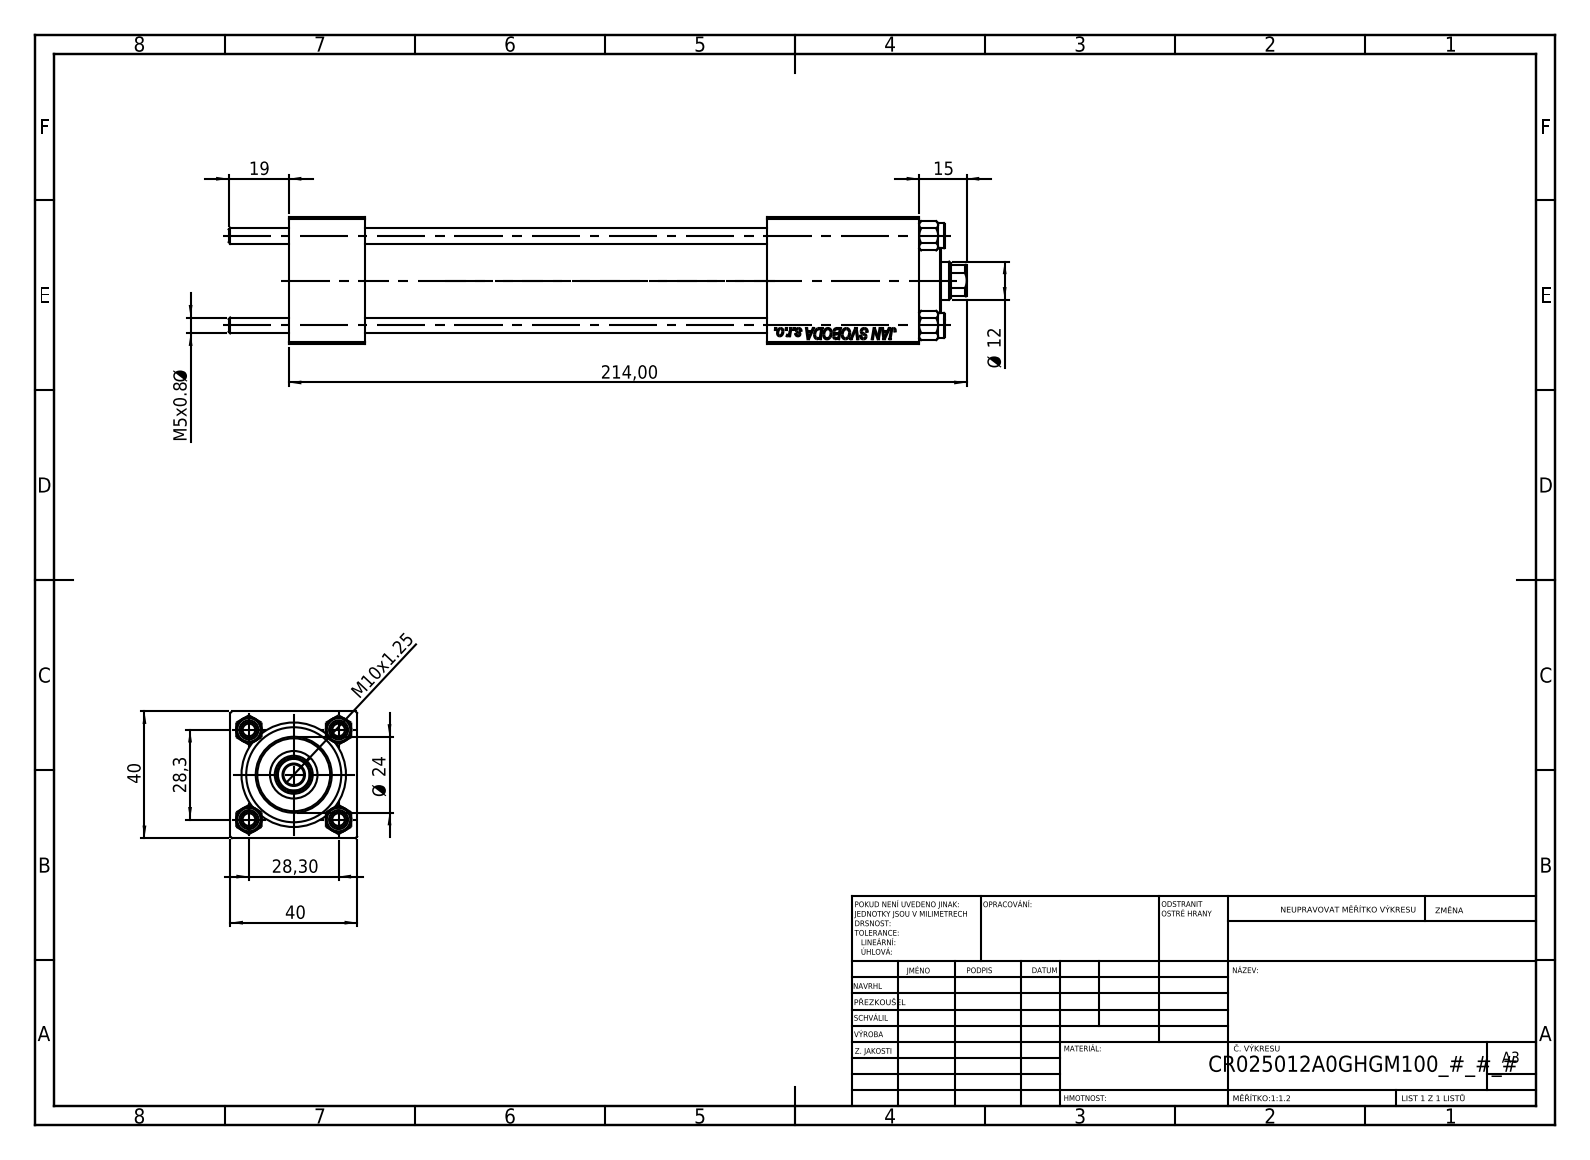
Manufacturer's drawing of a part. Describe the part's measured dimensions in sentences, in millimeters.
The part is named "CR025_012_A_0_G_A_G_M_020_+#_##_TYCINKA; NUT_M5; V215_VC_A; V215CR_BODY_A (+1 more)". Its 3-D file was written by "SolidWorks 2019 (CONFIG_CONTROL_DESIGN)". It is 11 solids with 1131 faces: 517 planar, 78 cylindrical and 536 other. Overall it measures 233 by 40 by 40 millimeters. Its volume is 181 266 cubic millimeters and its surface area 80 988 square millimeters. Round holes: 4 of diameter 5, 3 of diameter 20, 2 of diameter 7, 2 of diameter 13.16, 1 of diameter 6.5, 1 of diameter 12, 1 of diameter 15, 1 of diameter 25, 1 of diameter 30. Round bosses or shafts: 4 of diameter 8, 1 of diameter 31, 1 of diameter 24. Partial cylindrical surfaces (rounded edges, fillets, slot ends): 1 of radius 5.5. The main face-to-face distances are 40, 24, 199, 175, 170.3, 146.3, 28.7, 151, 127, 19.3. The hole center spacings are 20.01, 28.3, 40.02, 152.
